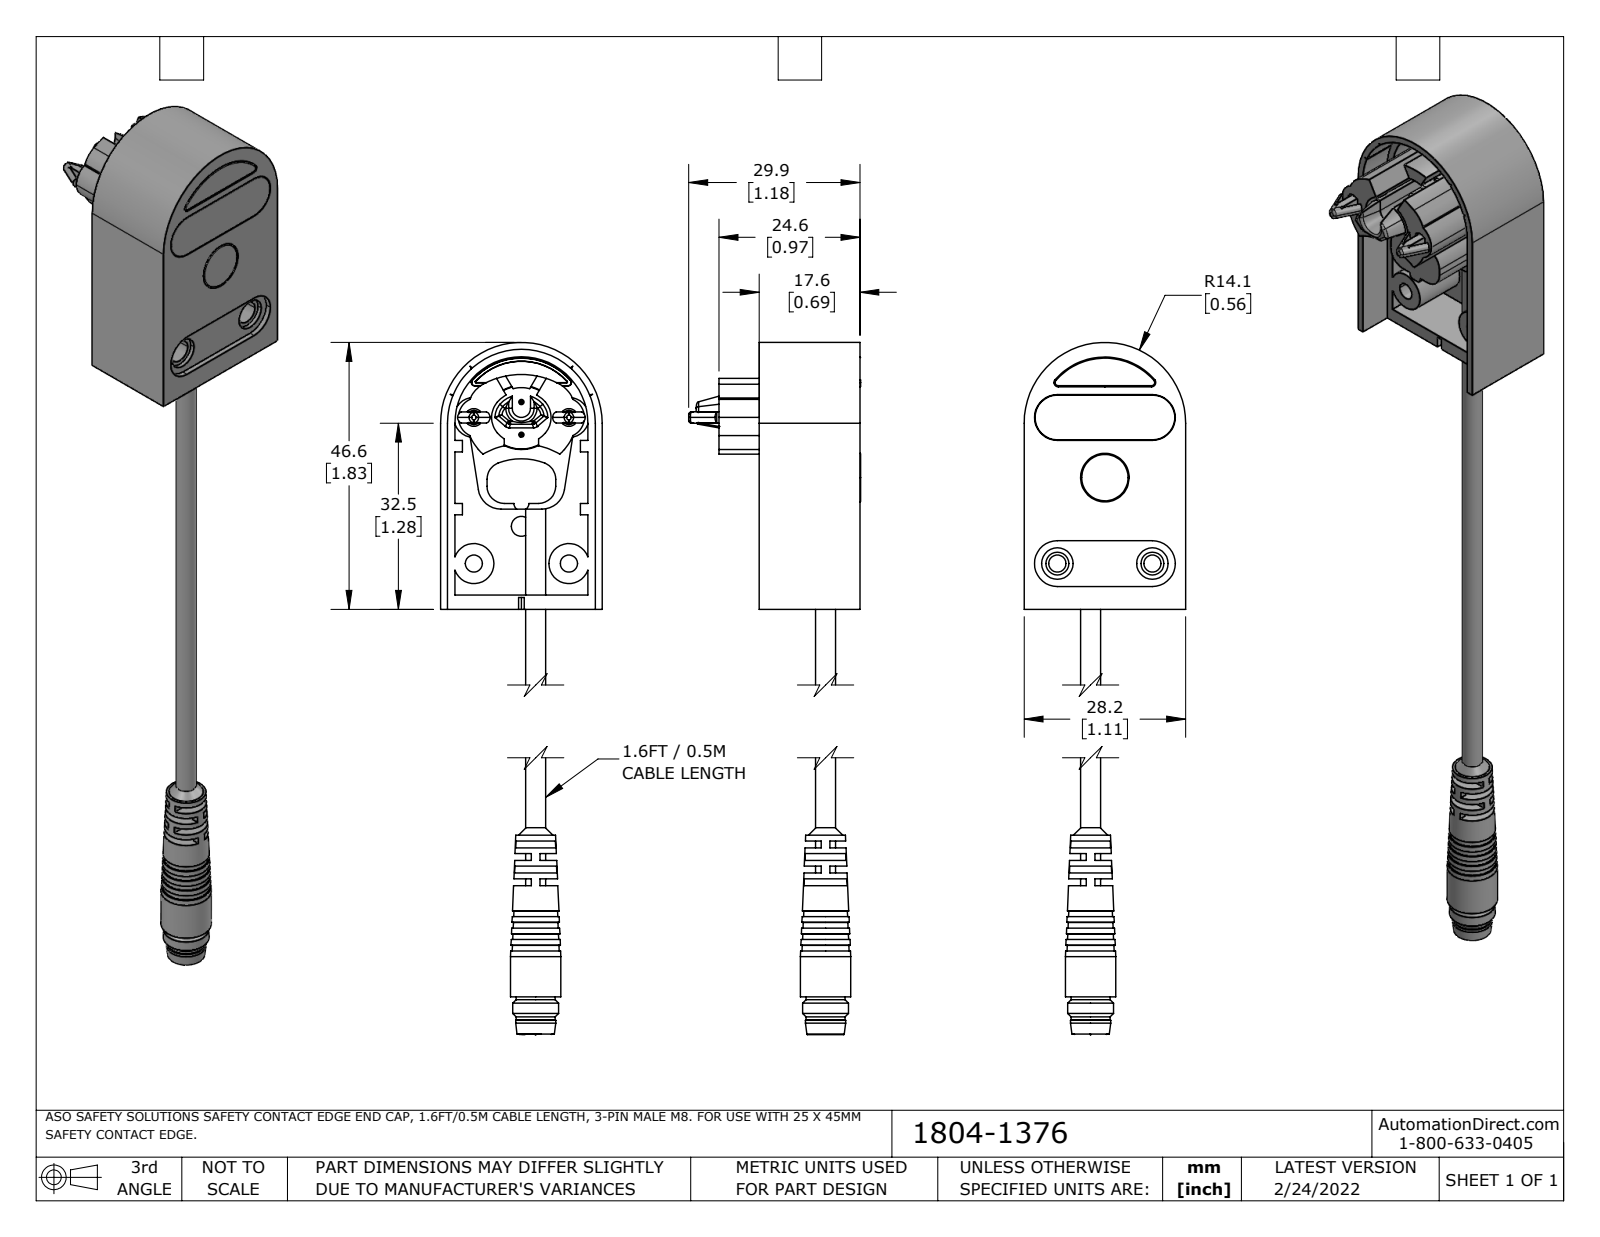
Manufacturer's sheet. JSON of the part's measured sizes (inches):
{"part_name": "1804-1376_Default", "step_written_by": "SolidWorks 2021 (CONFIG_CONTROL_DESIGN)", "units": "inches", "bodies": {"solids": 15, "faces": 729, "planar": 249, "cylindrical": 302, "other": 178}, "overall_size": [6.787, 1.181, 1.11], "volume_in3": 0.898, "surface_area_in2": 25.57, "round_holes": [[0.02, 4], [0.157, 4], [0.217, 4], [0.031, 3], [0.138, 3], [0.118, 2], [0.122, 2], [0.134, 1], [0.228, 1]], "round_bosses_or_shafts": [[0.047, 13], [0.02, 6], [0.276, 3], [0.138, 3], [0.039, 3], [0.197, 2], [0.098, 2], [0.079, 2]], "partial_cylinders_radius": [[0.039, 12], [0.004, 9], [0.012, 6], [0.118, 6], [0.138, 6], [0.157, 6], [0.02, 5], [0.197, 4]], "face_to_face_distances": [0.071, 0.098, 0.039, 1.11, 0.051, 0.047, 1.063, 1.012, 0.031, 0.965], "hole_center_spacings": [0.654, 0.055, 0.344, 0.348, 0.415, 0.816, 0.872, 0.892]}
